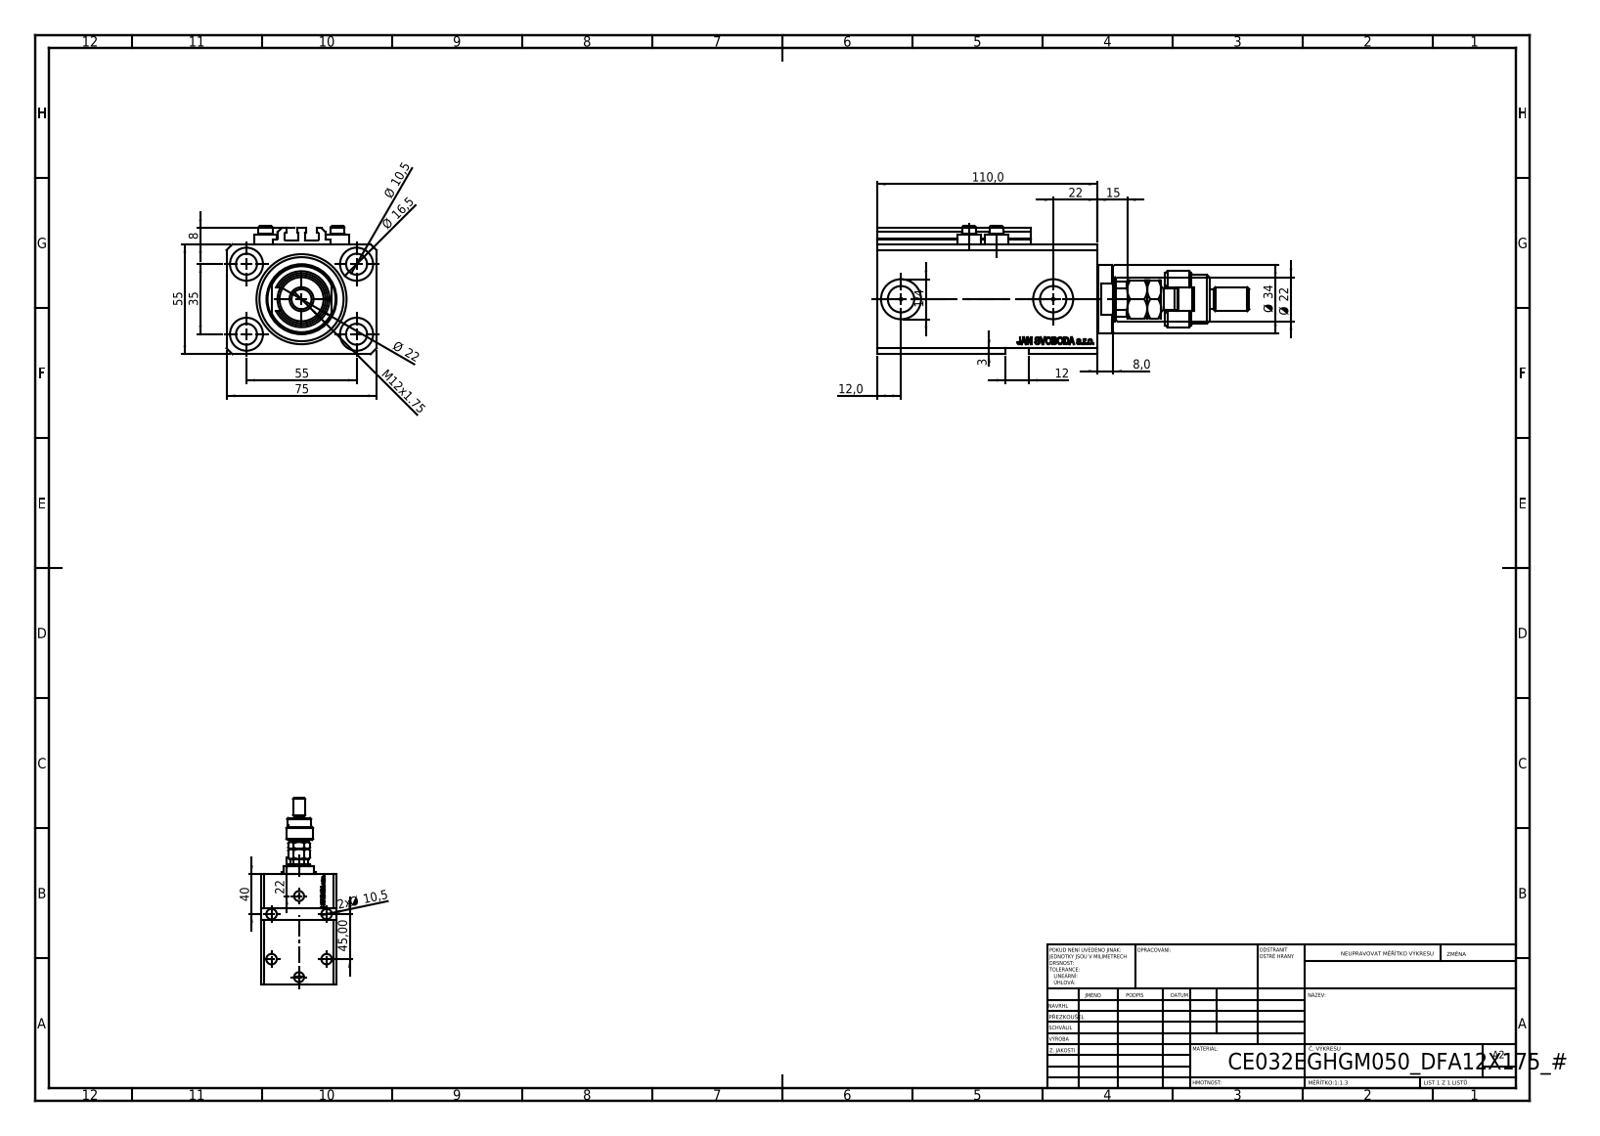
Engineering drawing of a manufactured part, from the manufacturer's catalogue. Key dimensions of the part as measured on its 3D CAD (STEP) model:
Part name (STEP PRODUCT): V250CE_C_VCP; V250CE_VC_E; ALLEN BOLT V250CE; MFA (+2 more)
STEP written by: SolidWorks 2019 (CONFIG_CONTROL_DESIGN)
Units: millimetres
Bodies: 10 solids, 1169 faces (542 planar, 159 cylindrical, 468 other)
Overall size (bounding box): 186 × 75 × 64
Volume: 399 218 mm³ · Surface area: 102 764 mm²
Round holes (diameter × count): ⌀10.5 ×9, ⌀1.25 ×4, ⌀4 ×4, ⌀16.5 ×4, ⌀10 ×2, ⌀13.16 ×2, ⌀20 ×2, ⌀22 ×1, ⌀32 ×1, ⌀45 ×1
Round bosses / shafts (diameter × count): ⌀11.6 ×4, ⌀7 ×4, ⌀34 ×1, ⌀28 ×1, ⌀24 ×1, ⌀18 ×1, ⌀12 ×1, ⌀11 ×1
Partial cylindrical surfaces — rounded edges, fillets, slot ends (radius × count): R0.2 ×10, R9.75 ×1, R10.5 ×1
Main face-to-face distances: 55, 75, 15, 110, 3, 95, 9.9, 8, 19, 85.1
Hole centre spacings: 32.6, 32.87, 55, 68.74, 13.6, 14.09, 23.05, 25.81
